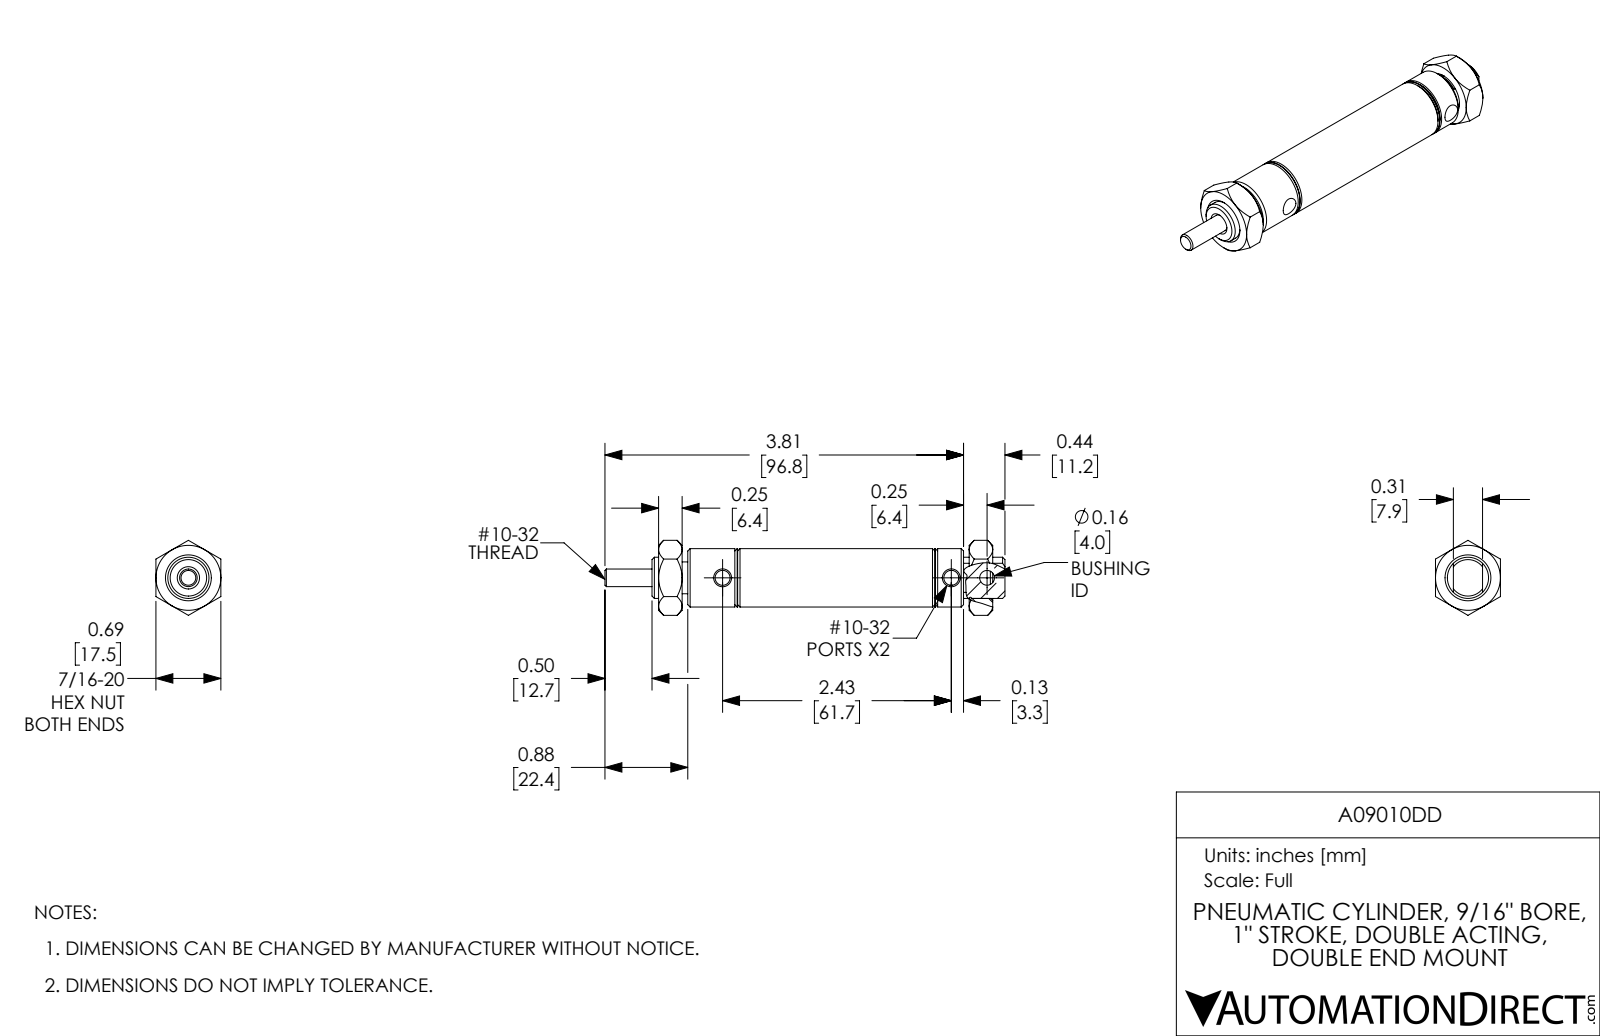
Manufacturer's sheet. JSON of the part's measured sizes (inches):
{"part_name": "A09010DD_Mounting Nut_D-154; A09010DD-Rod; A09010DD-MainBody; A09010DD", "step_written_by": "SolidWorks 2017 (AUTOMOTIVE_DESIGN)", "units": "inches", "bodies": {"solids": 4, "faces": 151, "planar": 36, "cylindrical": 46, "other": 69}, "overall_size": [4.25, 0.797, 0.69], "volume_in3": 0.876, "surface_area_in2": 17.64, "round_holes": [[0.159, 2], [0.19, 2], [0.156, 1], [0.157, 1], [0.187, 1], [0.563, 1]], "round_bosses_or_shafts": [[0.62, 1], [0.437, 1], [0.338, 1]], "face_to_face_distances": [0.69, 0.5, 0.25, 3.3, 0.715, 2.215, 2.275, 0.31, 1.5, 0.775], "hole_center_spacings": [0.38, 2.43, 2.81]}
